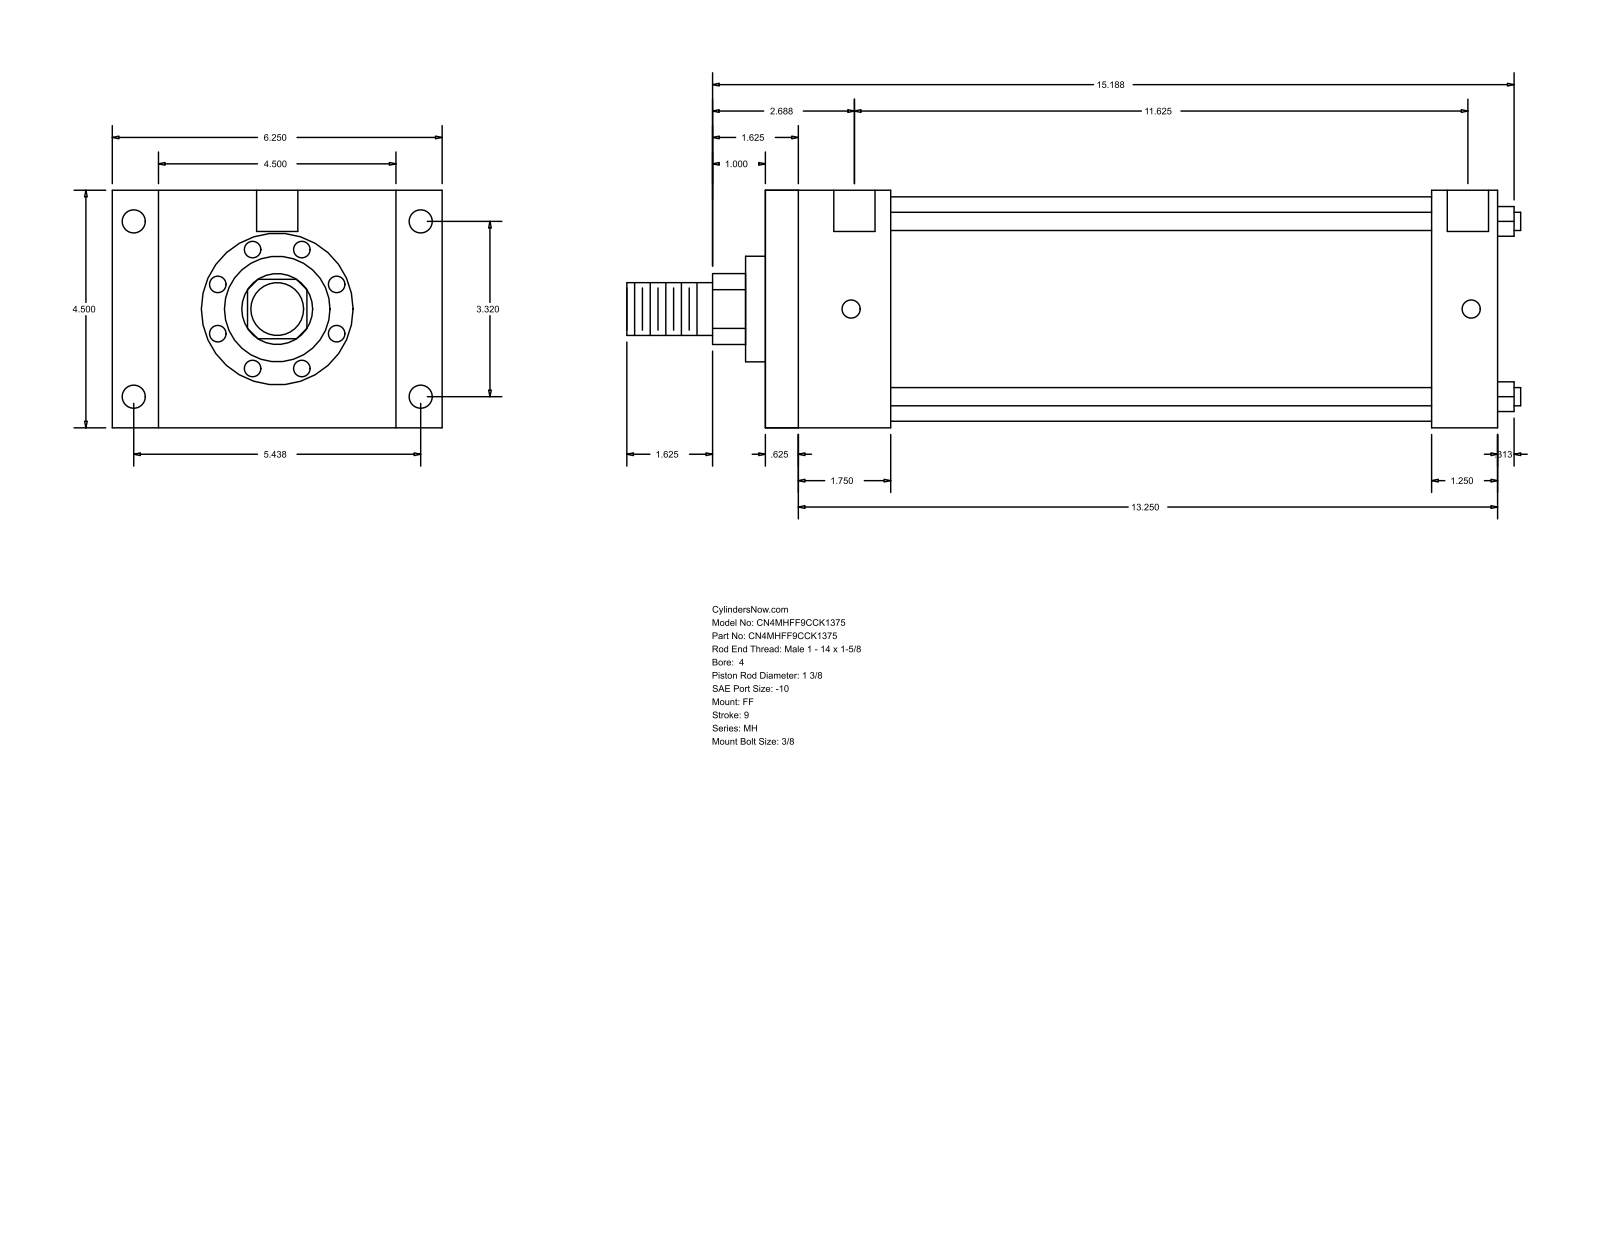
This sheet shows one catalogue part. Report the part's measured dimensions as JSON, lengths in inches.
{"part_name": "MH_FF__0400_1.375", "step_written_by": "GSSL Pune (CONFIG_CONTROL_DESIGN)", "units": "inches", "bodies": {"solids": 0, "faces": 92, "planar": 64, "cylindrical": 28, "other": 0}, "overall_size": [16.937, 6.25, 4.5], "round_holes": [[0.344, 4], [0.438, 4], [0.781, 2]], "round_bosses_or_shafts": [[0.345, 4], [4.25, 1], [2, 1], [1.375, 1], [1, 1]], "partial_cylinders_radius": [[0.672, 1]], "face_to_face_distances": [4.5, 13.875, 0.625, 13.25, 2.375, 1.75, 11.5, 12.625, 12, 10.25], "hole_center_spacings": [3.32, 5.438, 6.371, 11.75, 0.062, 0.063, 11.625, 11.687]}
